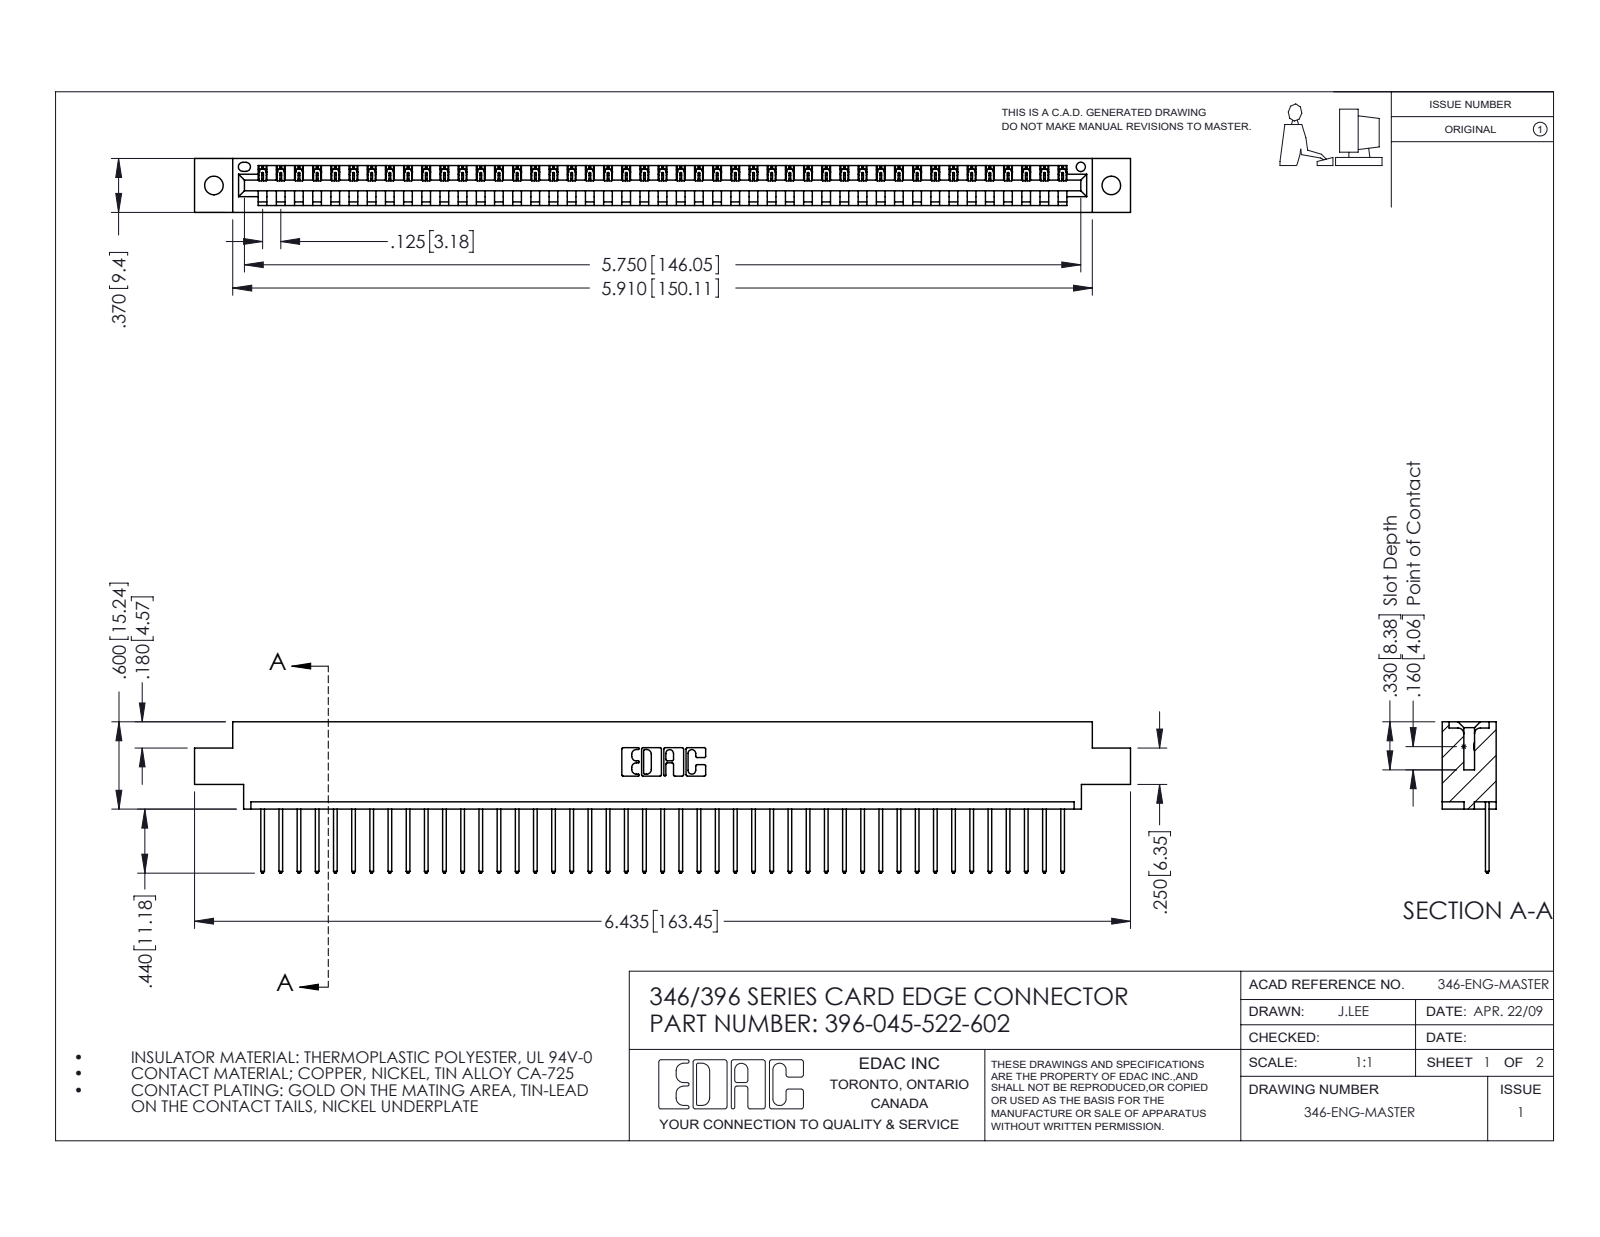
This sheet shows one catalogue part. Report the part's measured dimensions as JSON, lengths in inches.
{"part_name": "346 Part_0.170 Offset - 0.128 Dia; 345-292-001_345-293-122; 396-045-522-602", "step_written_by": "SolidWorks 2016 (CONFIG_CONTROL_DESIGN)", "units": "inches", "bodies": {"solids": 46, "faces": 2736, "planar": 1880, "cylindrical": 856, "other": 0}, "overall_size": [6.435, 1.04, 0.37], "volume_in3": 0.945, "surface_area_in2": 30.13, "round_holes": [[0.128, 2], [0.064, 1]], "partial_cylinders_radius": [[0.006, 90], [0.01, 90], [0.01, 22], [0.007, 6], [0.031, 6], [0.026, 3], [0.031, 2], [0.04, 2]], "face_to_face_distances": [0.048, 0.322, 0.37, 0.25, 0.072, 0.298, 0.025, 0.148, 0.222, 0.1], "hole_center_spacings": [0.246, 5.961, 6.17]}
